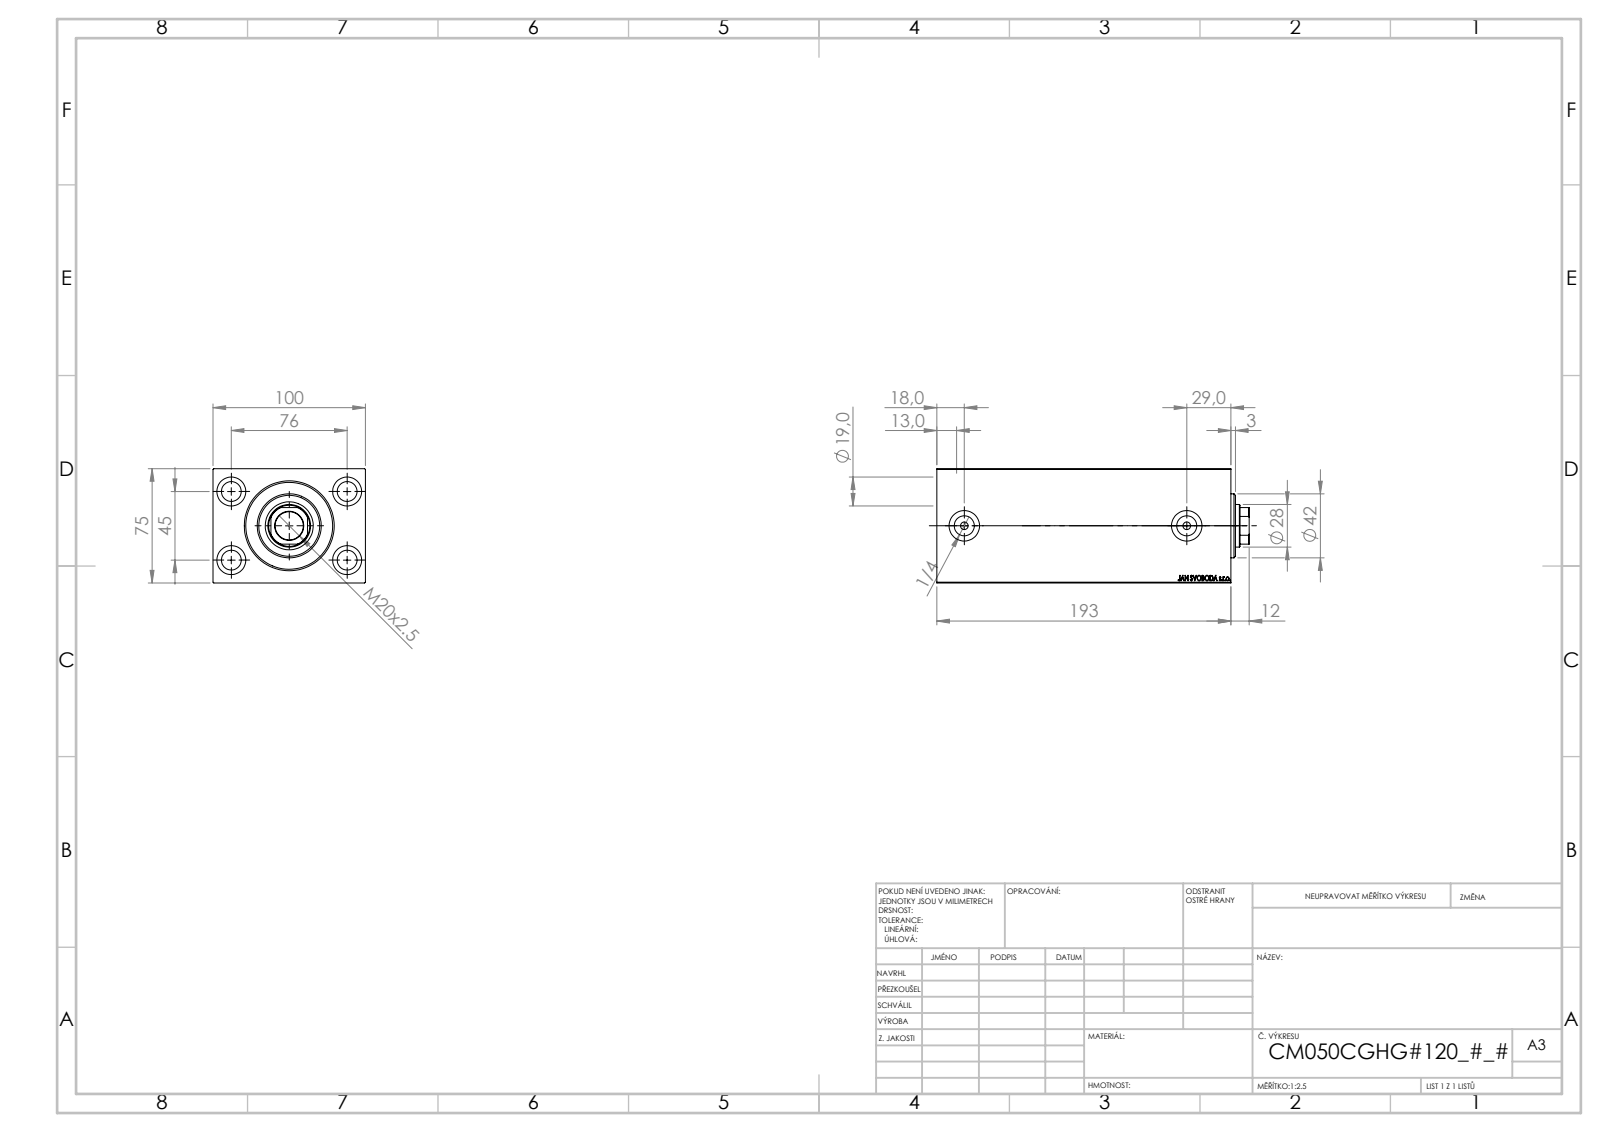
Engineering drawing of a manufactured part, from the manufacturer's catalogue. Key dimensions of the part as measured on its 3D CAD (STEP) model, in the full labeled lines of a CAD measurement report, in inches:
Part name (STEP PRODUCT): V450CM_VC_B; V450CM_C_Body; V450CM_C_VCP
STEP written by: SolidWorks 2019 (CONFIG_CONTROL_DESIGN)
Units: inches
Bodies: 3 solids, 865 faces (409 planar, 62 cylindrical, 394 other)
Overall size (bounding box): 8.071 × 3.937 × 2.953
Volume: 71.09 in³ · Surface area: 280 in²
Round holes (diameter × count): ⌀0.512 ×4, ⌀0.748 ×4, ⌀0.197 ×2, ⌀0.518 ×2, ⌀0.787 ×2, ⌀0.728 ×1, ⌀1.102 ×1, ⌀1.24 ×1, ⌀1.969 ×1, ⌀2.047 ×1, ⌀2.244 ×1
Round bosses / shafts (diameter × count): ⌀1.654 ×1
Partial cylindrical surfaces — rounded edges, fillets, slot ends (radius × count): R0.531 ×1
Main face-to-face distances: 2.953, 3.937, 7.598, 7.047, 0.551, 1.154, 5.894, 6.445, 0.512, 5.878
Hole centre spacings: 1.739, 1.772, 2.992, 3.477, 5.748
